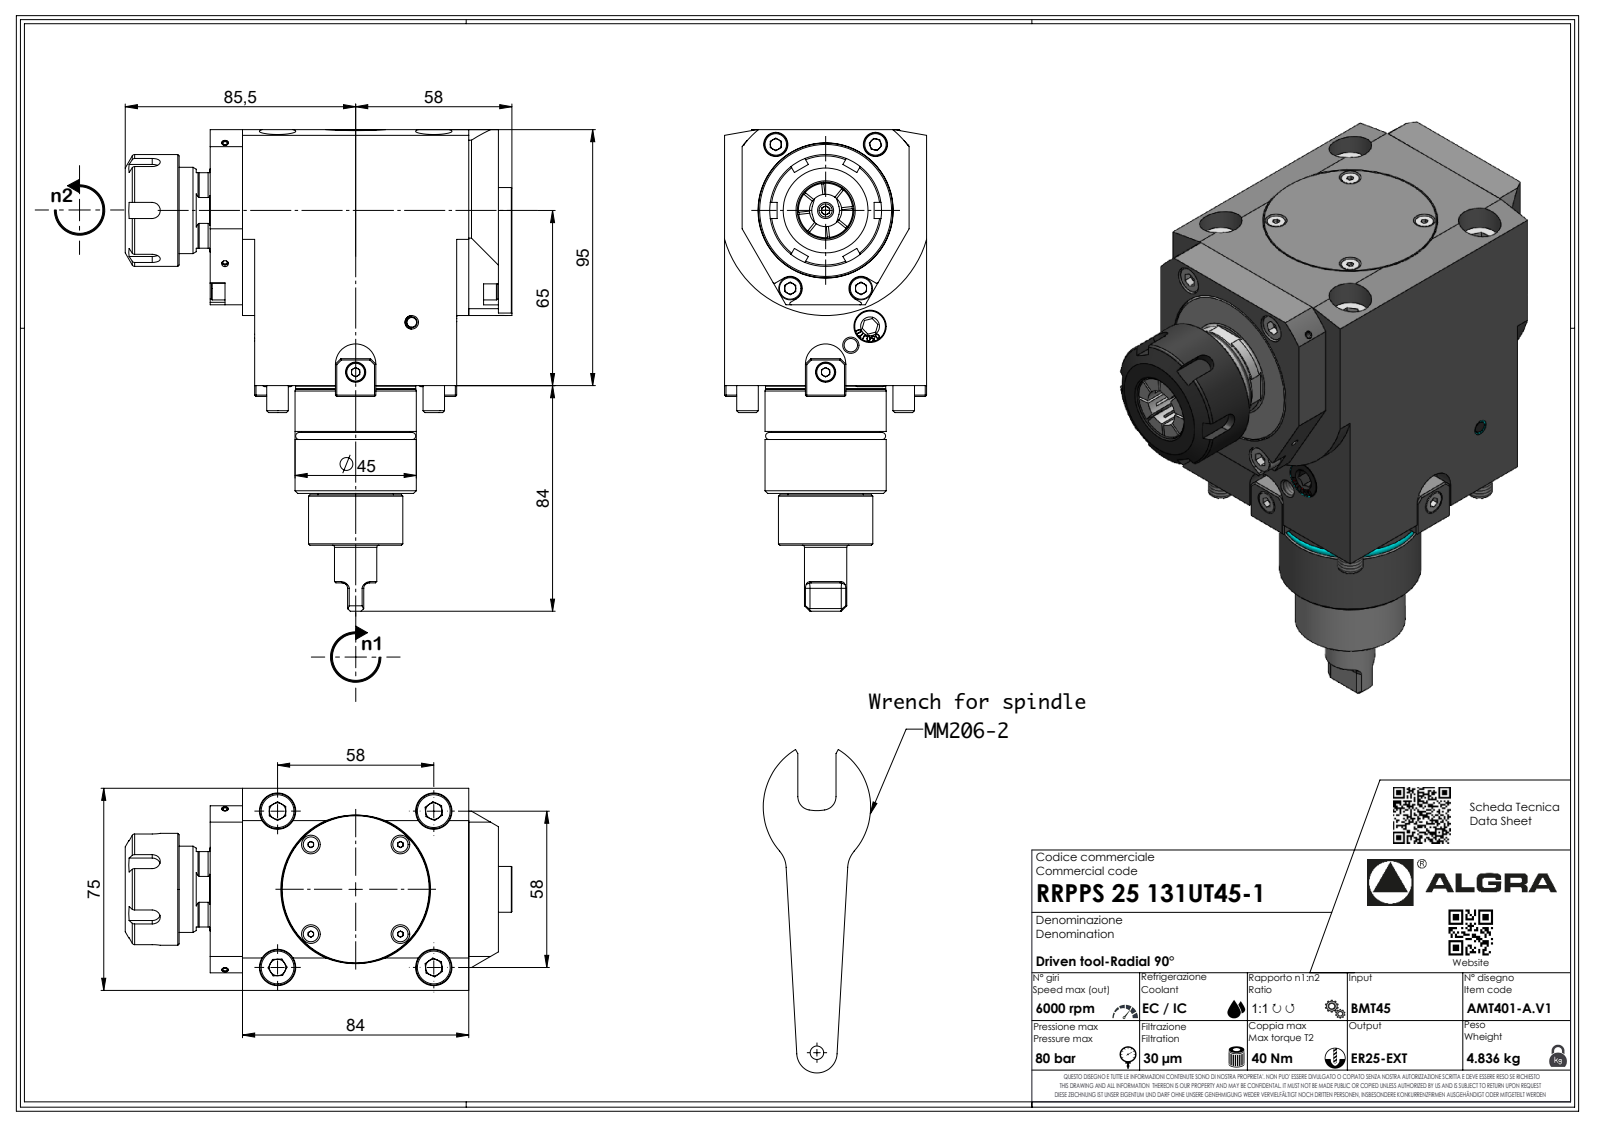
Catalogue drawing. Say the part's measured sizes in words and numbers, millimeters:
The part is named "RRPPS25131UT45-1". Its 3-D file was written by "SolidWorks 2023 (AUTOMOTIVE_DESIGN)". It is 1 solid with 662 faces: 431 planar, 99 cylindrical and 132 other. Overall it measures 178.7 by 143.38 by 75 millimeters. Its volume is 762 928 cubic millimeters and its surface area 71 616 square millimeters. Round holes: 1 of diameter 2.1, 1 of diameter 38.2, 1 of diameter 42.2, 1 of diameter 46.2, 1 of diameter 50.2, 1 of diameter 54. Round bosses or shafts: 4 of diameter 8, 1 of diameter 50, 1 of diameter 46, 1 of diameter 45, 1 of diameter 44.6, 1 of diameter 42, 1 of diameter 41.5, 1 of diameter 40.2. Partial cylindrical surfaces (rounded edges, fillets, slot ends): 7 of radius 0.33, 7 of radius 0.52, 7 of radius 3.7, 6 of radius 0.5, 6 of radius 2, 5 of radius 3, 4 of radius 4.5, 2 of radius 4.5. The main face-to-face distances are 75, 95, 4.5, 16.35, 91.35, 79.5, 15.5, 106.85, 90.5, 20.
